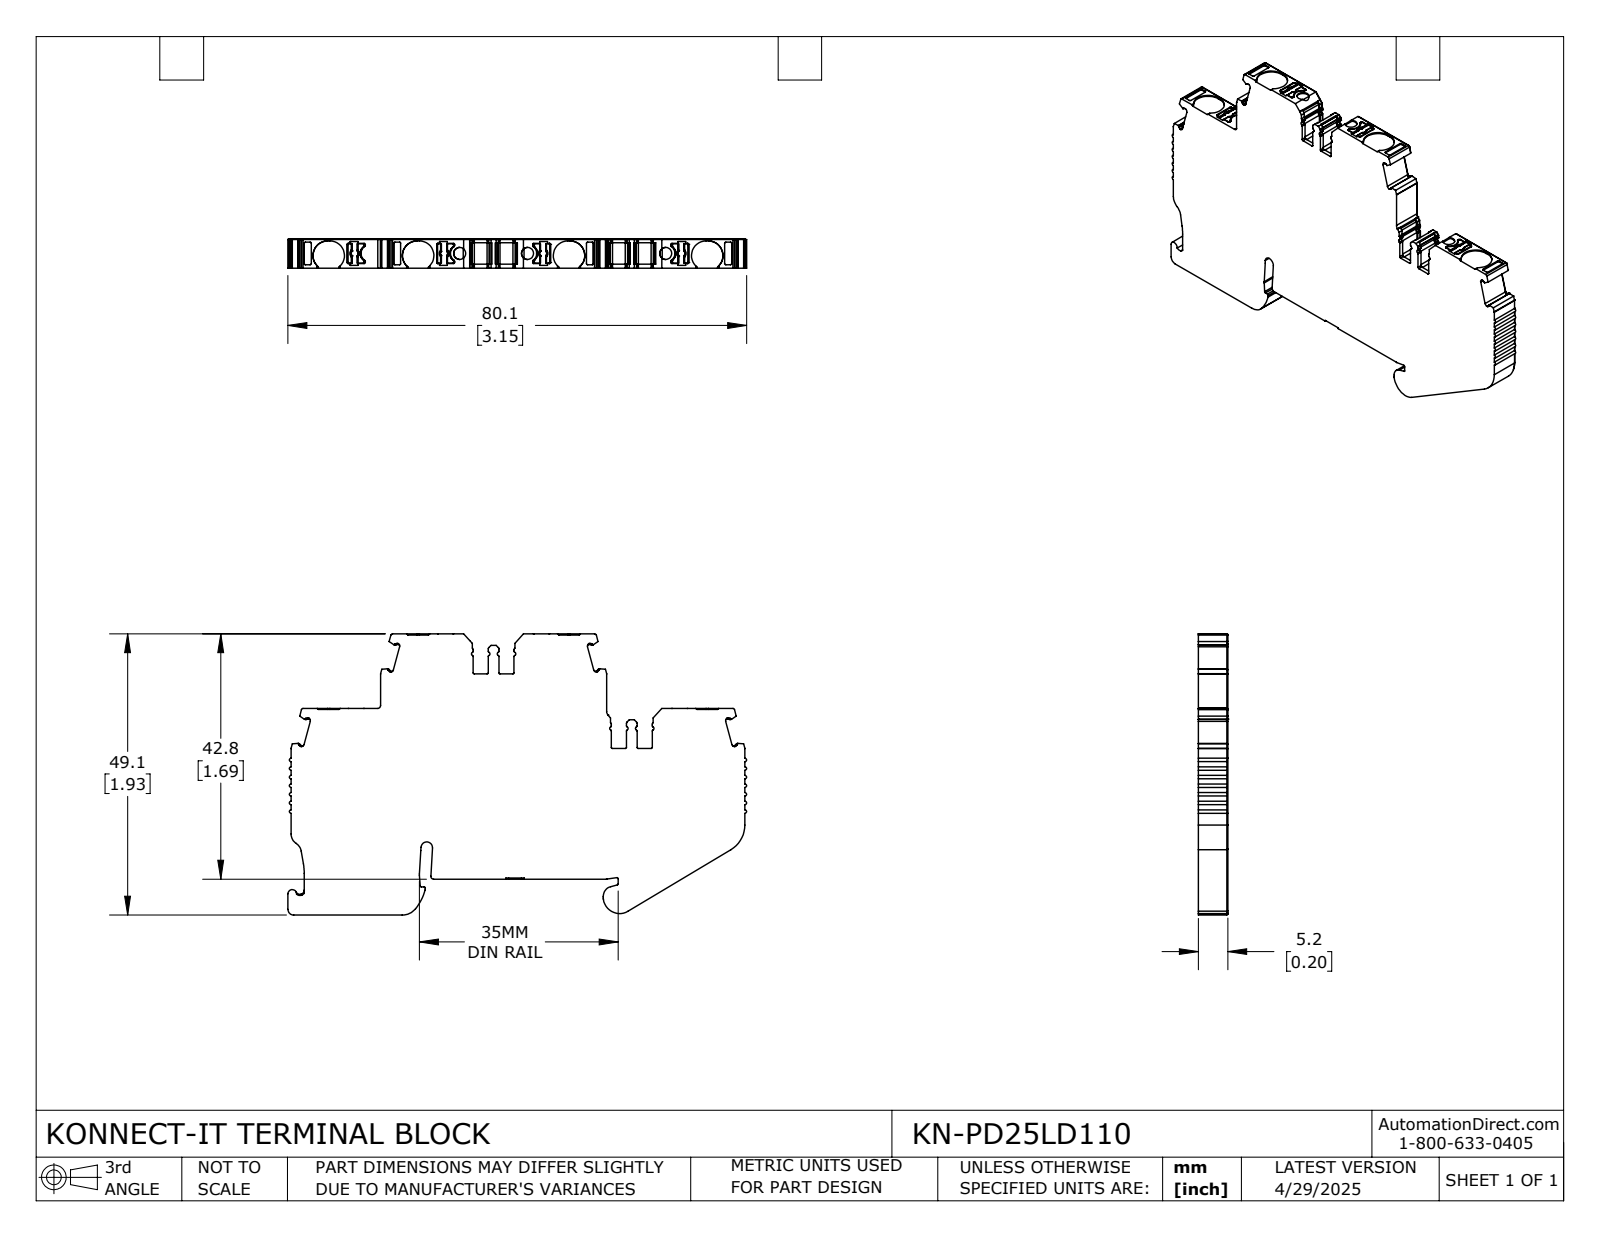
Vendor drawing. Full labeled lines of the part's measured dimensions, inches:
Part name (STEP PRODUCT): KN-PD25LD110
STEP written by: SolidWorks 2024 (CONFIG_CONTROL_DESIGN)
Units: inches
Bodies: 1 solid, 979 faces (470 planar, 438 cylindrical, 71 other)
Overall size (bounding box): 3.153 × 1.933 × 0.203
Volume: 0.889 in³ · Surface area: 11.63 in²
Round holes (diameter × count): ⌀0.083 ×3
Partial cylindrical surfaces — rounded edges, fillets, slot ends (radius × count): R0.008 ×100, R0.012 ×57, R0.004 ×41, R0.02 ×21, R0.016 ×17, R0.006 ×16, R0.024 ×9, R0.006 ×8
Main face-to-face distances: 0.203, 0.512, 0.246, 1.678, 1.166, 1.924, 0.079, 1.412, 0.504, 0.95
Hole centre spacings: 0.466, 0.95, 1.417
